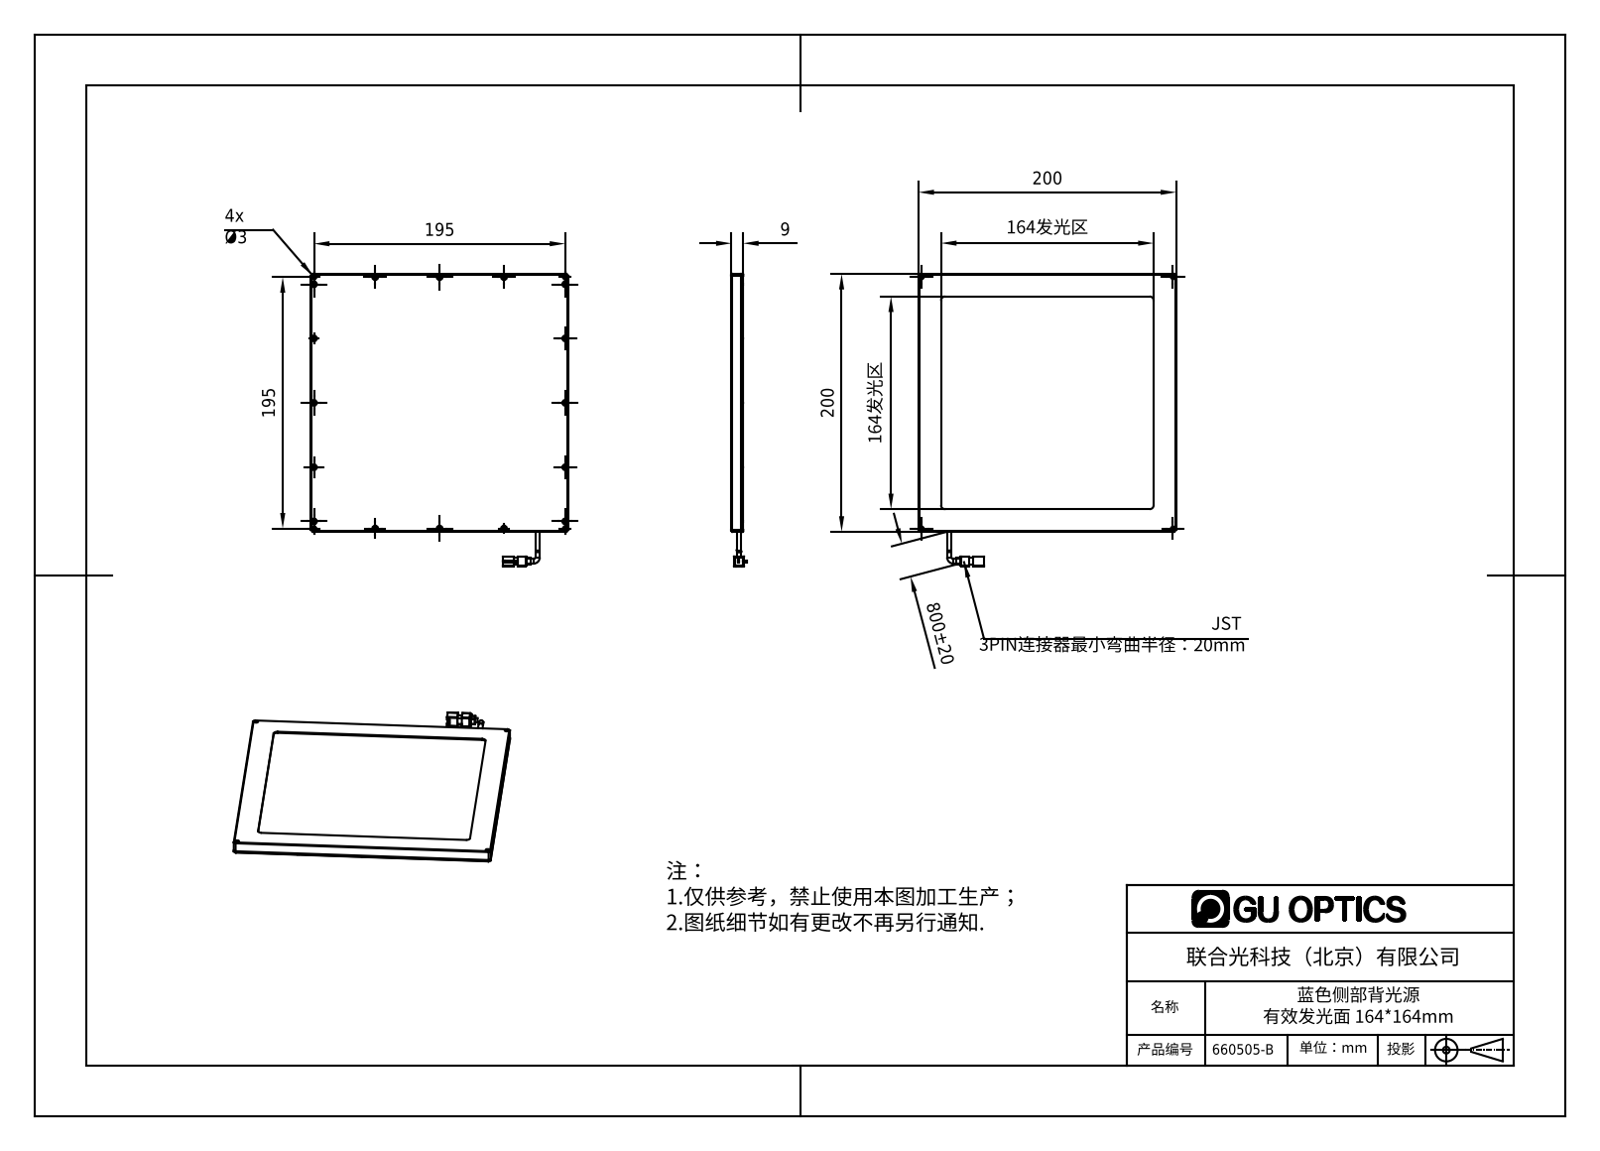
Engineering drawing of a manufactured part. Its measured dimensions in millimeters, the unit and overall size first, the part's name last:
Units: millimetres
Overall size (bounding box): 227 × 200 × 11.8
Round holes (diameter × count): ⌀1.6 ×16, ⌀2.4 ×16, ⌀2 ×8, ⌀3 ×4, ⌀3.3 ×4
Round bosses / shafts (diameter × count): ⌀3.5 ×2
Partial cylindrical surfaces — rounded edges, fillets, slot ends (radius × count): R0.5 ×8, R3 ×8, R1.5 ×6, R1 ×4, R1.6 ×1
Main face-to-face distances: 4, 6.5, 8, 1.5, 2.5, 7.5, 1, 5, 9, 196
Hole centre spacings: 195, 47.5, 50, 97.5, 108.46, 147.5, 154.96, 176.81
Volume: 224 961 mm³ · Surface area: 192 480 mm²
Bodies: 7 solids, 732 faces (472 planar, 134 cylindrical, 126 other)
Part name (STEP PRODUCT): 660505-B
STEP written by: SolidWorks 2016 (AUTOMOTIVE_DESIGN)
